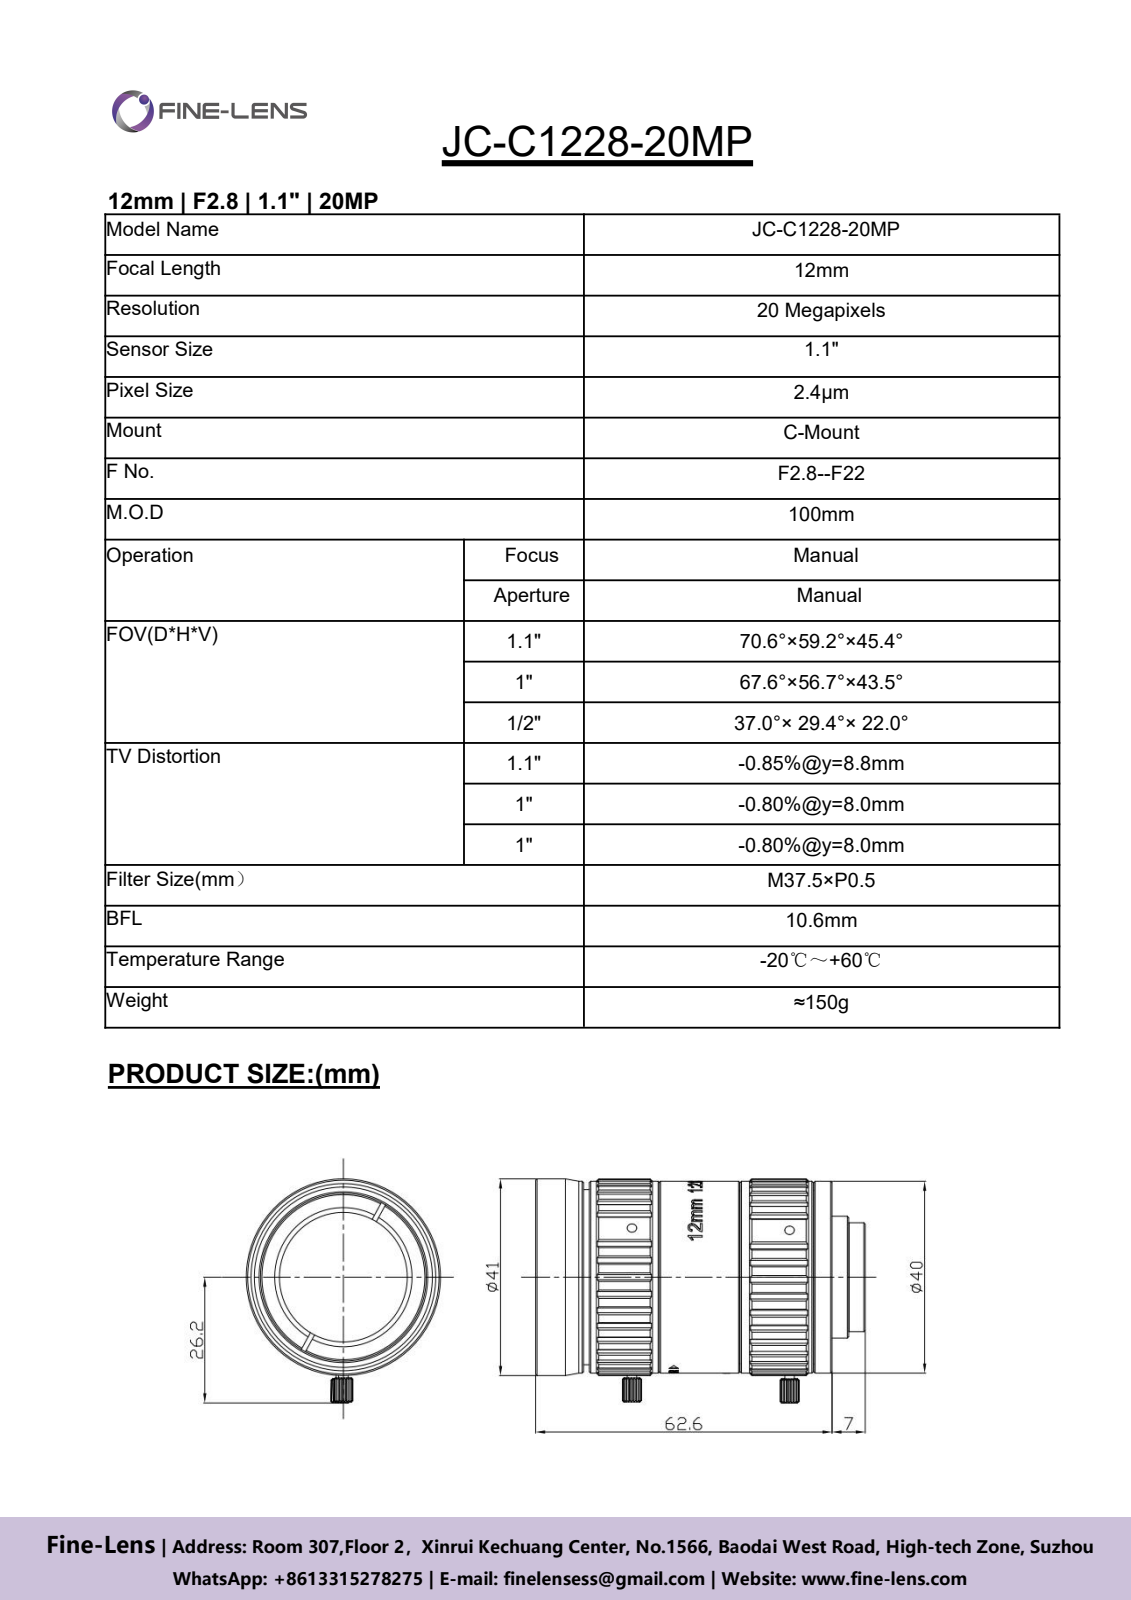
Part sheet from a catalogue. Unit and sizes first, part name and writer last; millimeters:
Units: millimetres
Overall size (bounding box): 69.6 × 47.7 × 41
Round holes (diameter × count): ⌀2 ×6, ⌀2.7 ×6, ⌀1.2 ×5, ⌀1.8 ×3, ⌀13.5 ×1, ⌀18 ×1, ⌀22 ×1, ⌀22.6 ×1, ⌀27 ×1, ⌀28.5 ×1, ⌀31.4 ×1, ⌀33.4 ×1
Round bosses / shafts (diameter × count): ⌀2.5 ×4, ⌀2 ×3, ⌀1.7 ×3, ⌀1.4 ×2, ⌀41 ×1, ⌀40 ×1, ⌀36.5 ×1, ⌀36.2 ×1
Partial cylindrical surfaces — rounded edges, fillets, slot ends (radius × count): R0.5 ×2, R2 ×2, R6.43 ×2, R17.25 ×1, R19.9 ×1, R19.95 ×1, R20.2 ×1
Main face-to-face distances: 33.05, 14.53, 47.58, 5, 8.39, 41.44, 55.97, 17, 53.99, 45.6
Hole centre spacings: 24.69, 3.02, 8.25, 14.25, 6, 6.42, 8.62, 9.38
Volume: 60 153 mm³ · Surface area: 28 214 mm²
Bodies: 4 solids, 1295 faces (461 planar, 345 cylindrical, 489 other)
Part name (STEP PRODUCT): 12MM1_1INCH_ASM; 12MM1_1INCH_ASM_ASM
STEP written by: CREO PARAMETRIC BY PTC INC, 2020053 (CONFIG_CONTROL_DESIGN)
